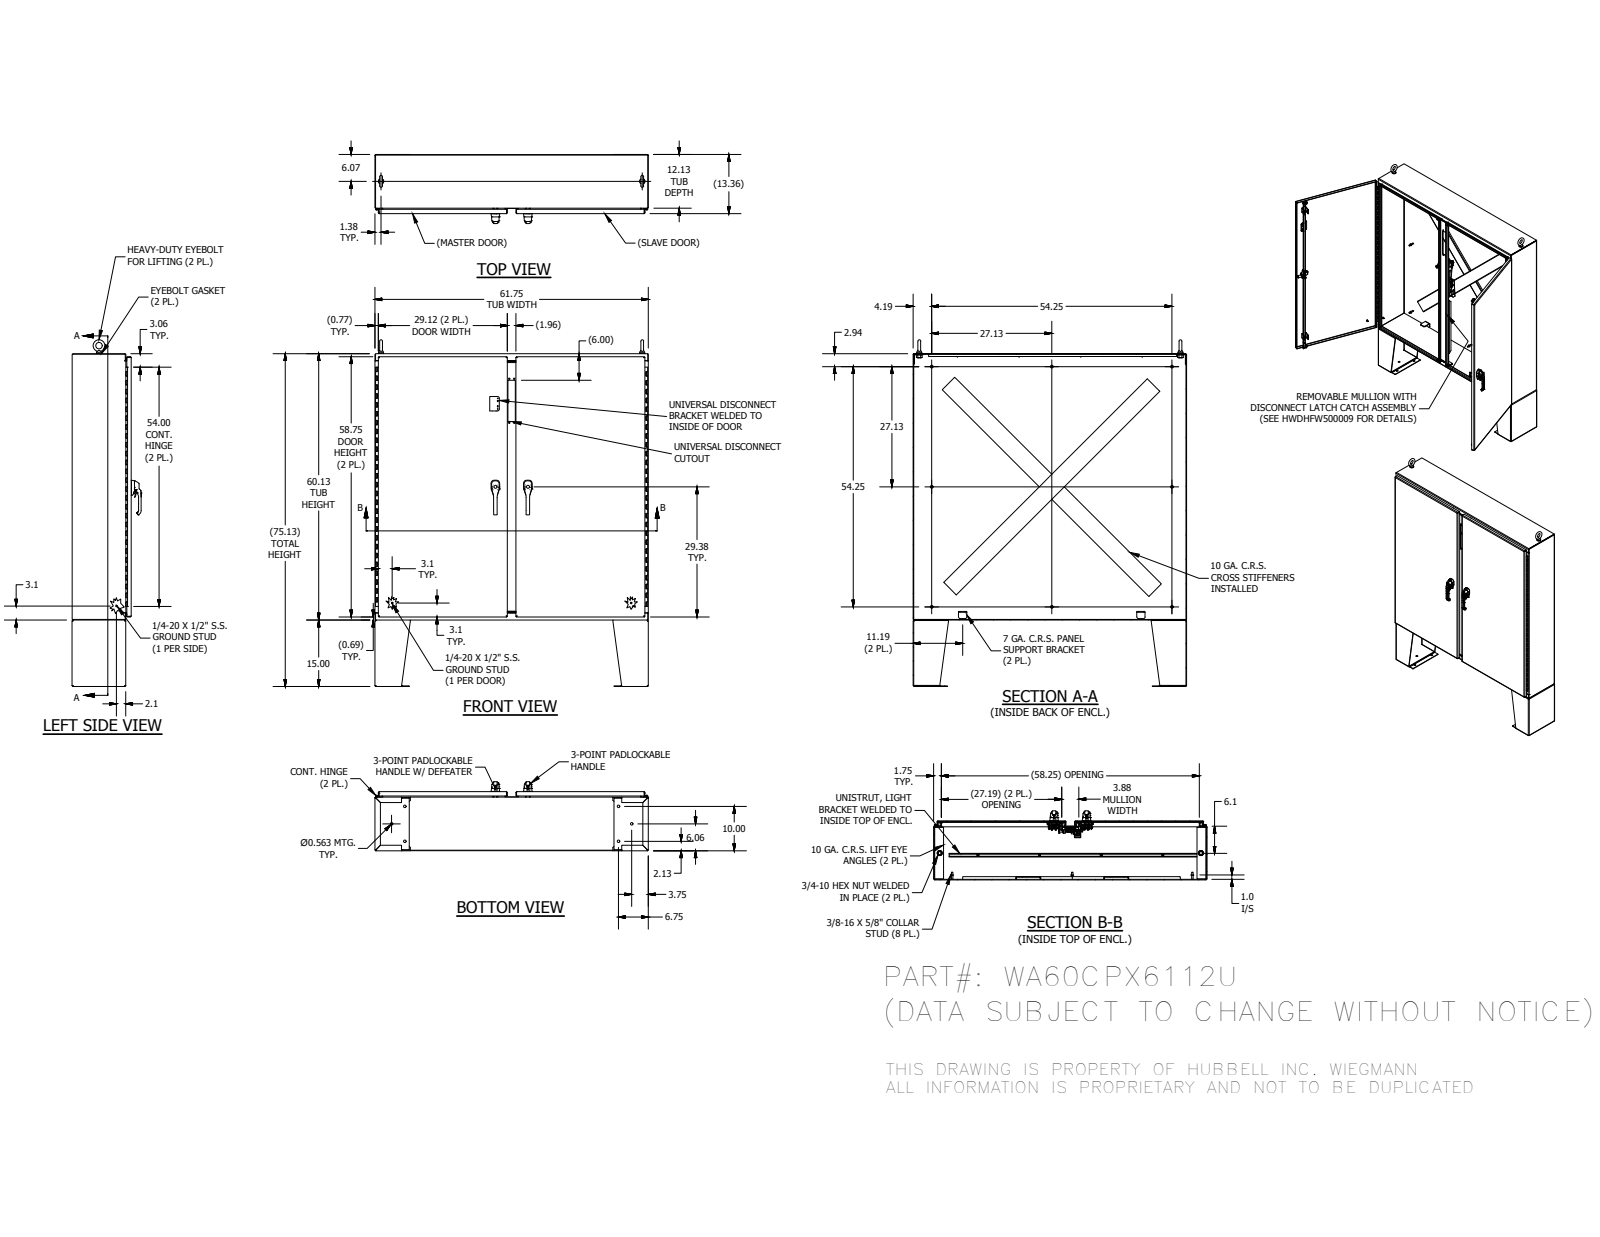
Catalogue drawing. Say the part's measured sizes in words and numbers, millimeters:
The part is named "WA60CPX6112UBLR; WACPX6112UTOP; WACPX6112UBTM; 30364 (+8 more)". Its 3-D file was written by "Autodesk Inventor 2016 (AUTOMOTIVE_DESIGN)". It is 210 solids with 8527 faces: 3961 planar, 2849 cylindrical and 1717 other. Overall it measures 1987.49 by 1568.45 by 396.45 millimeters. Its volume is 30 140 000 cubic millimeters and its surface area 18 500 000 square millimeters. Round holes: 21 of diameter 6.35, 18 of diameter 9.52, 18 of diameter 14.29, 8 of diameter 5.08, 8 of diameter 5.16, 8 of diameter 7.02, 8 of diameter 7.94, 6 of diameter 3.96, 6 of diameter 4.83, 6 of diameter 4.98, 6 of diameter 5.11, 6 of diameter 5.4. Round bosses or shafts: 18 of diameter 6.35, 16 of diameter 8.38, 14 of diameter 15.88, 9 of diameter 14.29, 9 of diameter 9.52, 9 of diameter 8.56, 8 of diameter 25.4, 8 of diameter 11.13. Partial cylindrical surfaces (rounded edges, fillets, slot ends): 344 of radius 0.5, 202 of radius 0.3, 144 of radius 0.51, 42 of radius 0.47, 40 of radius 1.27, 40 of radius 3.17, 37 of radius 2.38, 27 of radius 2. The main face-to-face distances are 3.4, 335.7, 332.3, 339.1, 3.41, 1523.77, 3.18, 1565.04, 304.57, 288.47. The hole center spacings are 27.99, 186.28, 70.08, 187.63, 22.5, 29, 30.36, 32.29.
